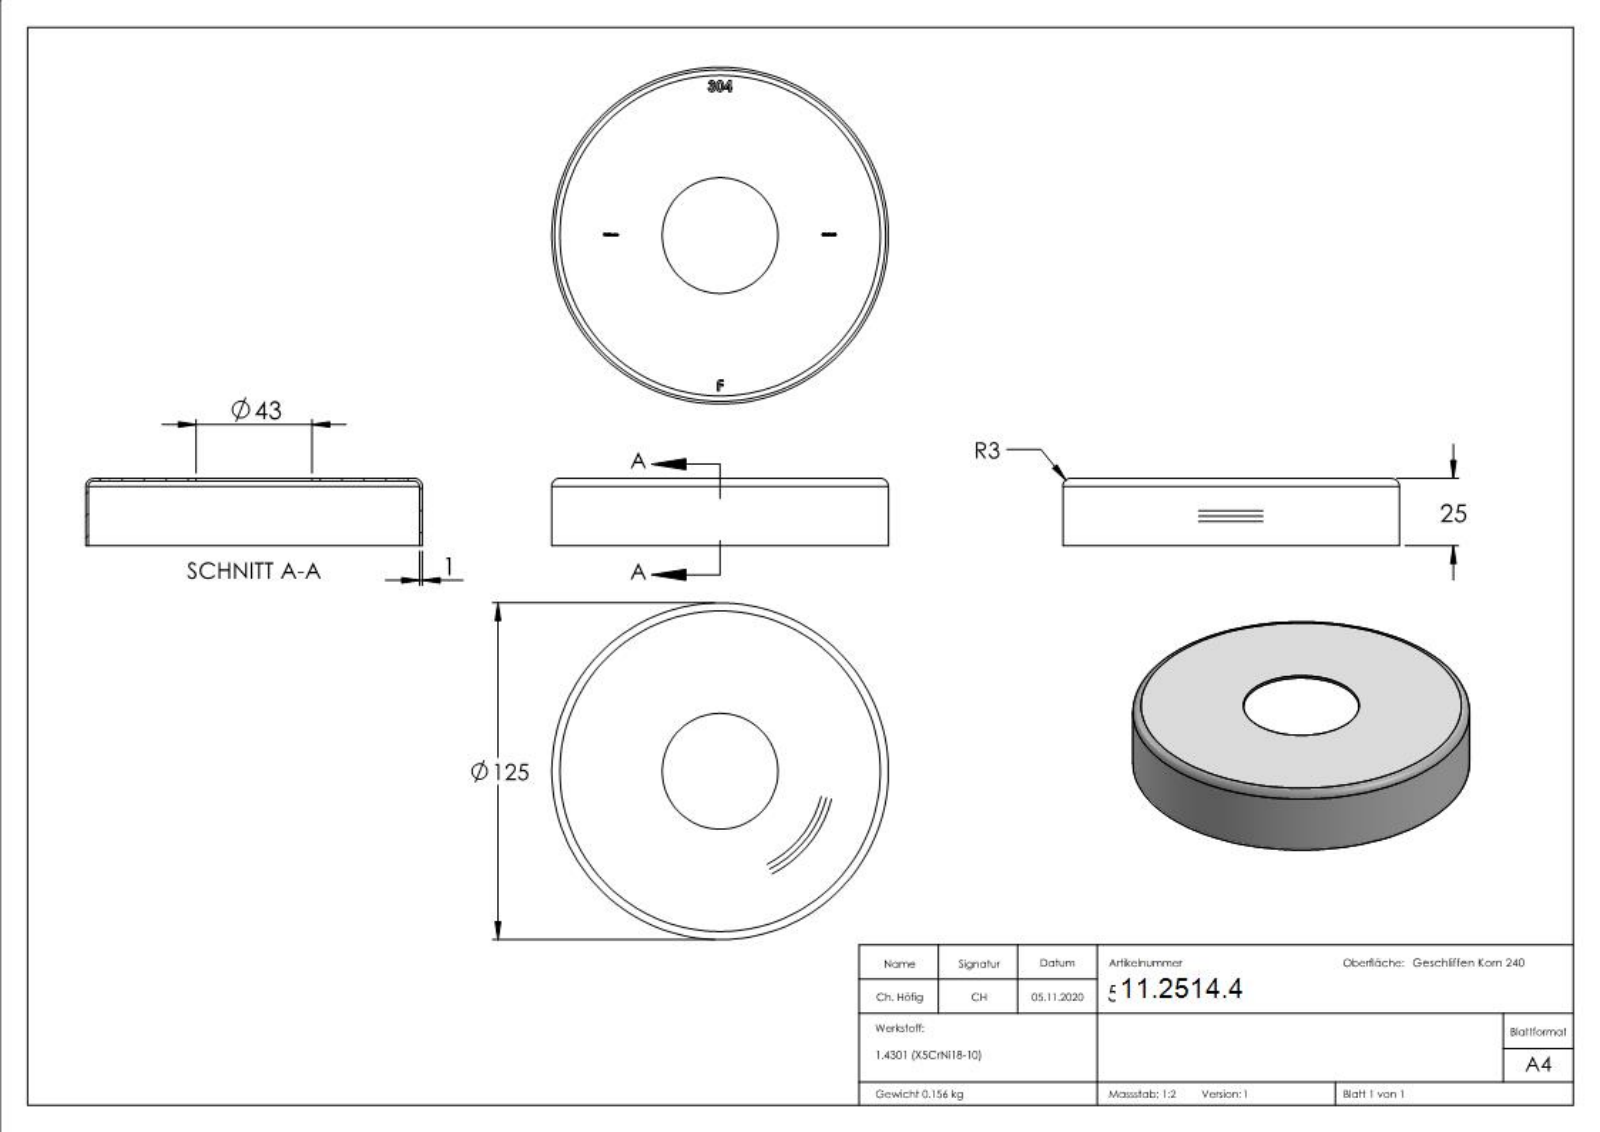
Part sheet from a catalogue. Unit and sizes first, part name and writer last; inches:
Units: inches
Overall size (bounding box): 4.921 × 4.921 × 0.984
Round holes (diameter × count): ⌀1.693 ×1, ⌀4.843 ×1
Round bosses / shafts (diameter × count): ⌀4.921 ×1
Main face-to-face distances: 0.039, 0.945, 0.984, 0.949, 0.035, 0.028, 0.197, 0.169, 0.023, 0.027
Volume: 1.205 in³ · Surface area: 62.05 in²
Bodies: 1 solid, 300 faces (159 planar, 6 cylindrical, 135 other)
Part name (STEP PRODUCT): 50840-240
STEP written by: SolidWorks 2018 (CONFIG_CONTROL_DESIGN)
